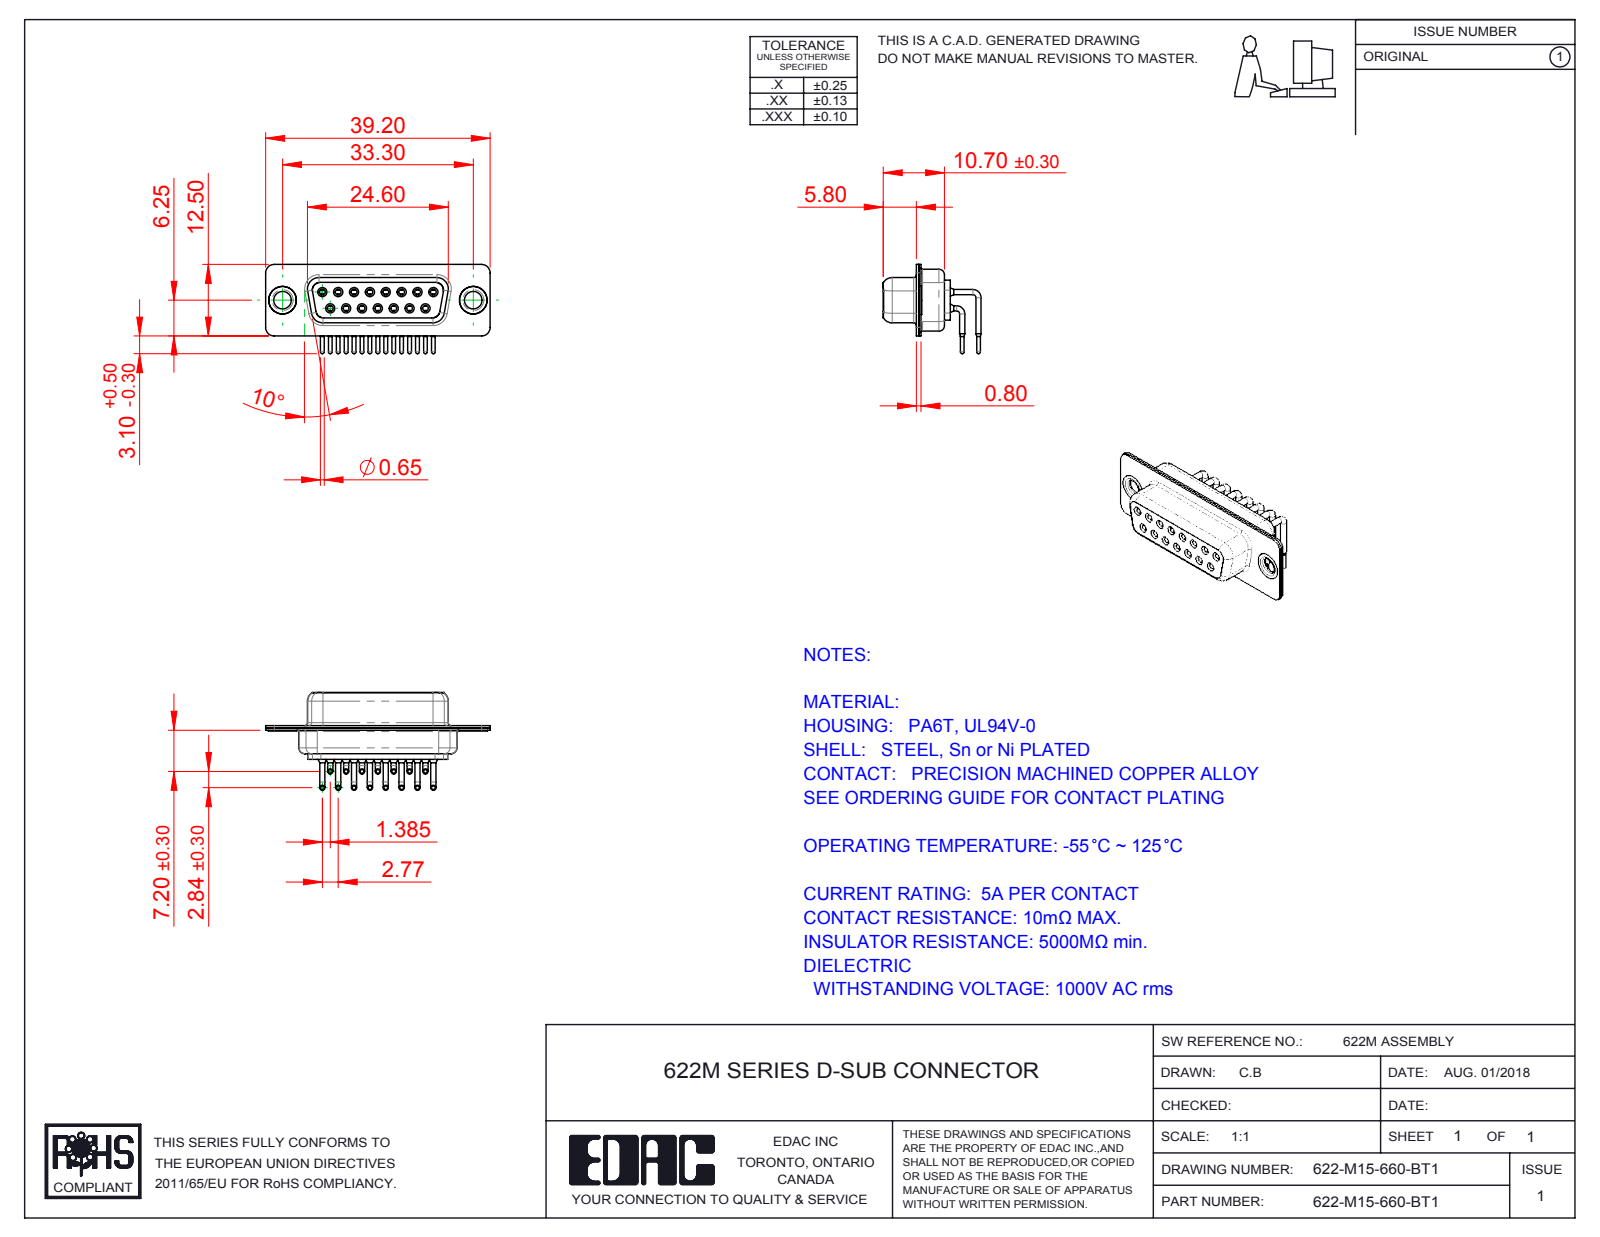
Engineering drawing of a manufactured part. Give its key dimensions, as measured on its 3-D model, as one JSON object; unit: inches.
{"part_name": "622M Shell Front_15 Contacts; 622-M15-660-BT1; 622M Thru Hole Rivet; 622M Housing_15 Contacts (+3 more)", "step_written_by": "SolidWorks 2016 (CONFIG_CONTROL_DESIGN)", "units": "inches", "bodies": {"solids": 20, "faces": 1048, "planar": 292, "cylindrical": 466, "other": 290}, "overall_size": [1.543, 0.673, 0.614], "volume_in3": 0.15, "surface_area_in2": 9.715, "round_holes": [[0.039, 15], [0.043, 15], [0.067, 15], [0.071, 15], [0.079, 15], [0.12, 2], [0.157, 2], [0.189, 2]], "round_bosses_or_shafts": [[0.035, 30], [0.063, 15], [0.059, 15], [0.026, 15], [0.197, 2], [0.193, 2], [0.14, 2]], "partial_cylinders_radius": [[0.059, 16], [0.079, 12], [0.053, 8], [0.063, 8], [0.01, 4], [0.02, 4], [0.024, 4], [0.026, 4]], "face_to_face_distances": [0.016, 0.057, 0.352, 0.244, 0.075, 0.335, 0.091, 0.018, 0.278, 0.033], "hole_center_spacings": [0.124, 0.109, 0.218, 0.327, 0.436, 0.198, 0.198, 0.294]}
